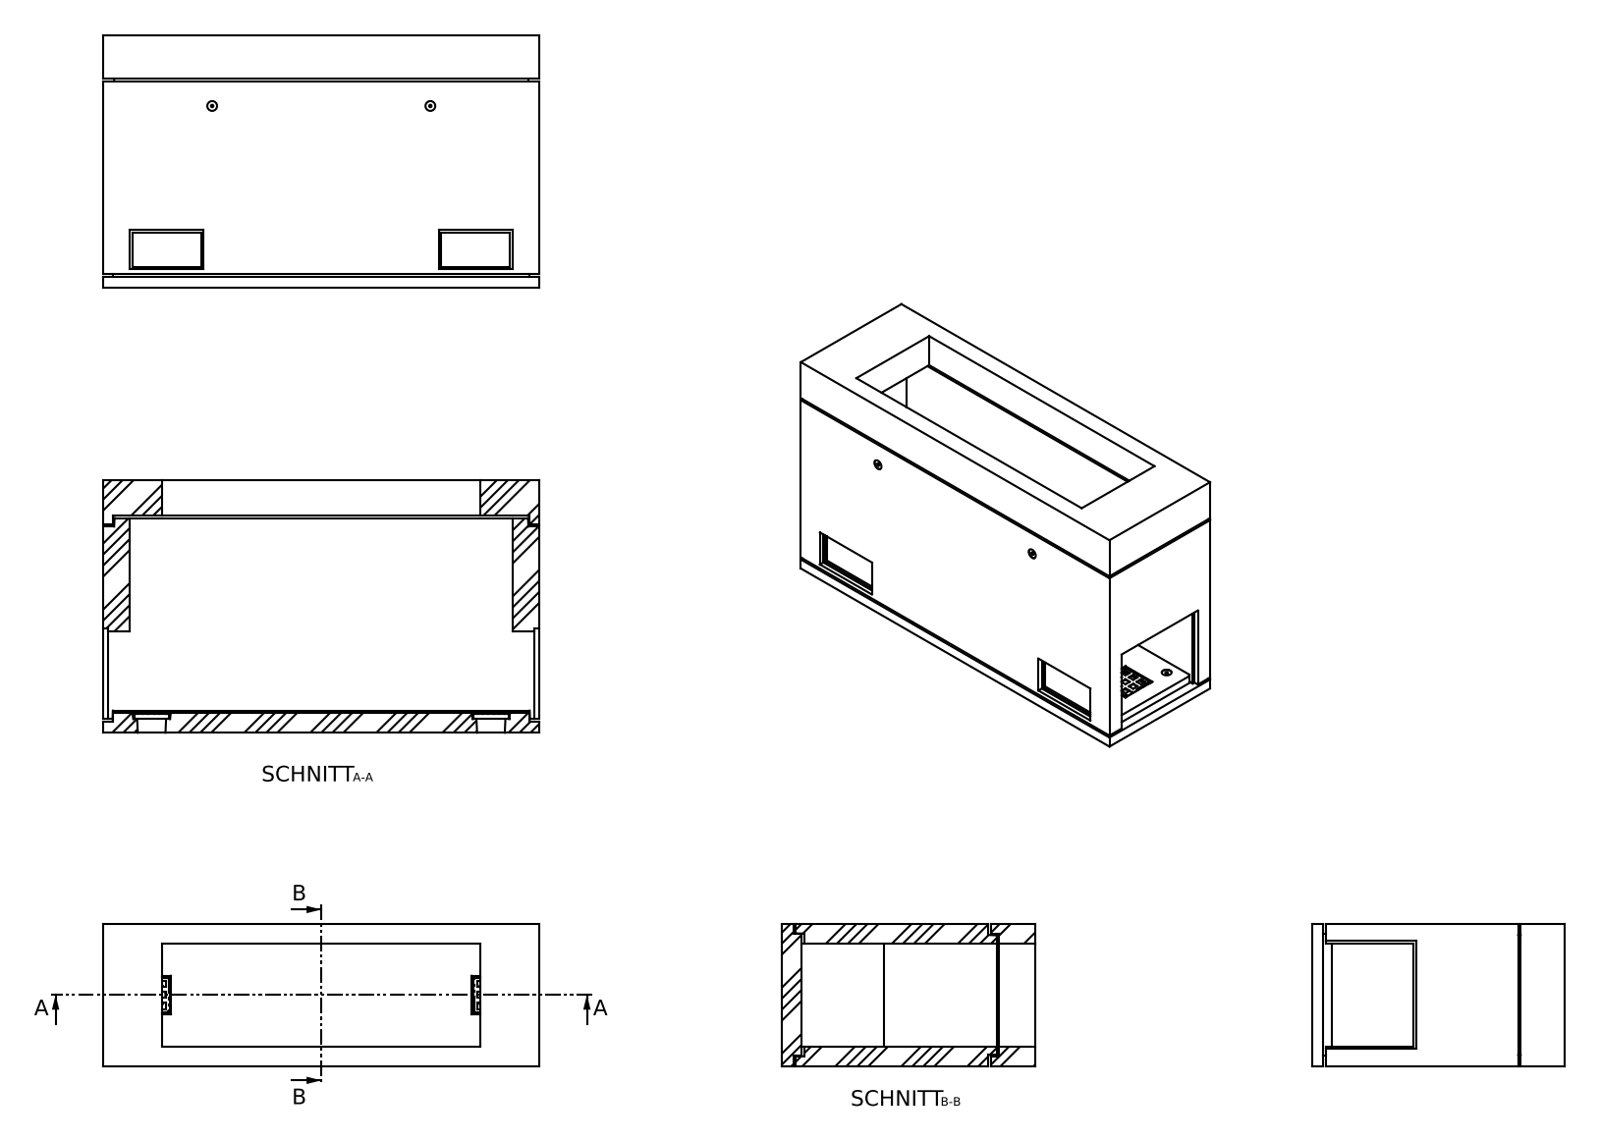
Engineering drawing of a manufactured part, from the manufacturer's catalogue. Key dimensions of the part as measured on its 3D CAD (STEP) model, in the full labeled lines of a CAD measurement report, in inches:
Part name (STEP PRODUCT): SC-A15.0416.15.103
STEP written by: SolidWorks 2018 (AUTOMOTIVE_DESIGN)
Units: inches
Bodies: 0 solids, 225 faces (163 planar, 40 cylindrical, 22 other)
Overall size (bounding box): 70.079 × 40.591 × 22.835
Round holes (diameter × count): ⌀1.575 ×6
Round bosses / shafts (diameter × count): ⌀0.394 ×6, ⌀0.229 ×6
Partial cylindrical surfaces — rounded edges, fillets, slot ends (radius × count): R0.079 ×6, R0.157 ×6
Main face-to-face distances: 3.15, 19.685, 22.835, 16.535, 31.339, 40.591, 37.441, 0.394, 70.079, 4.331
Hole centre spacings: 12.992, 60.236, 61.621, 35.039
